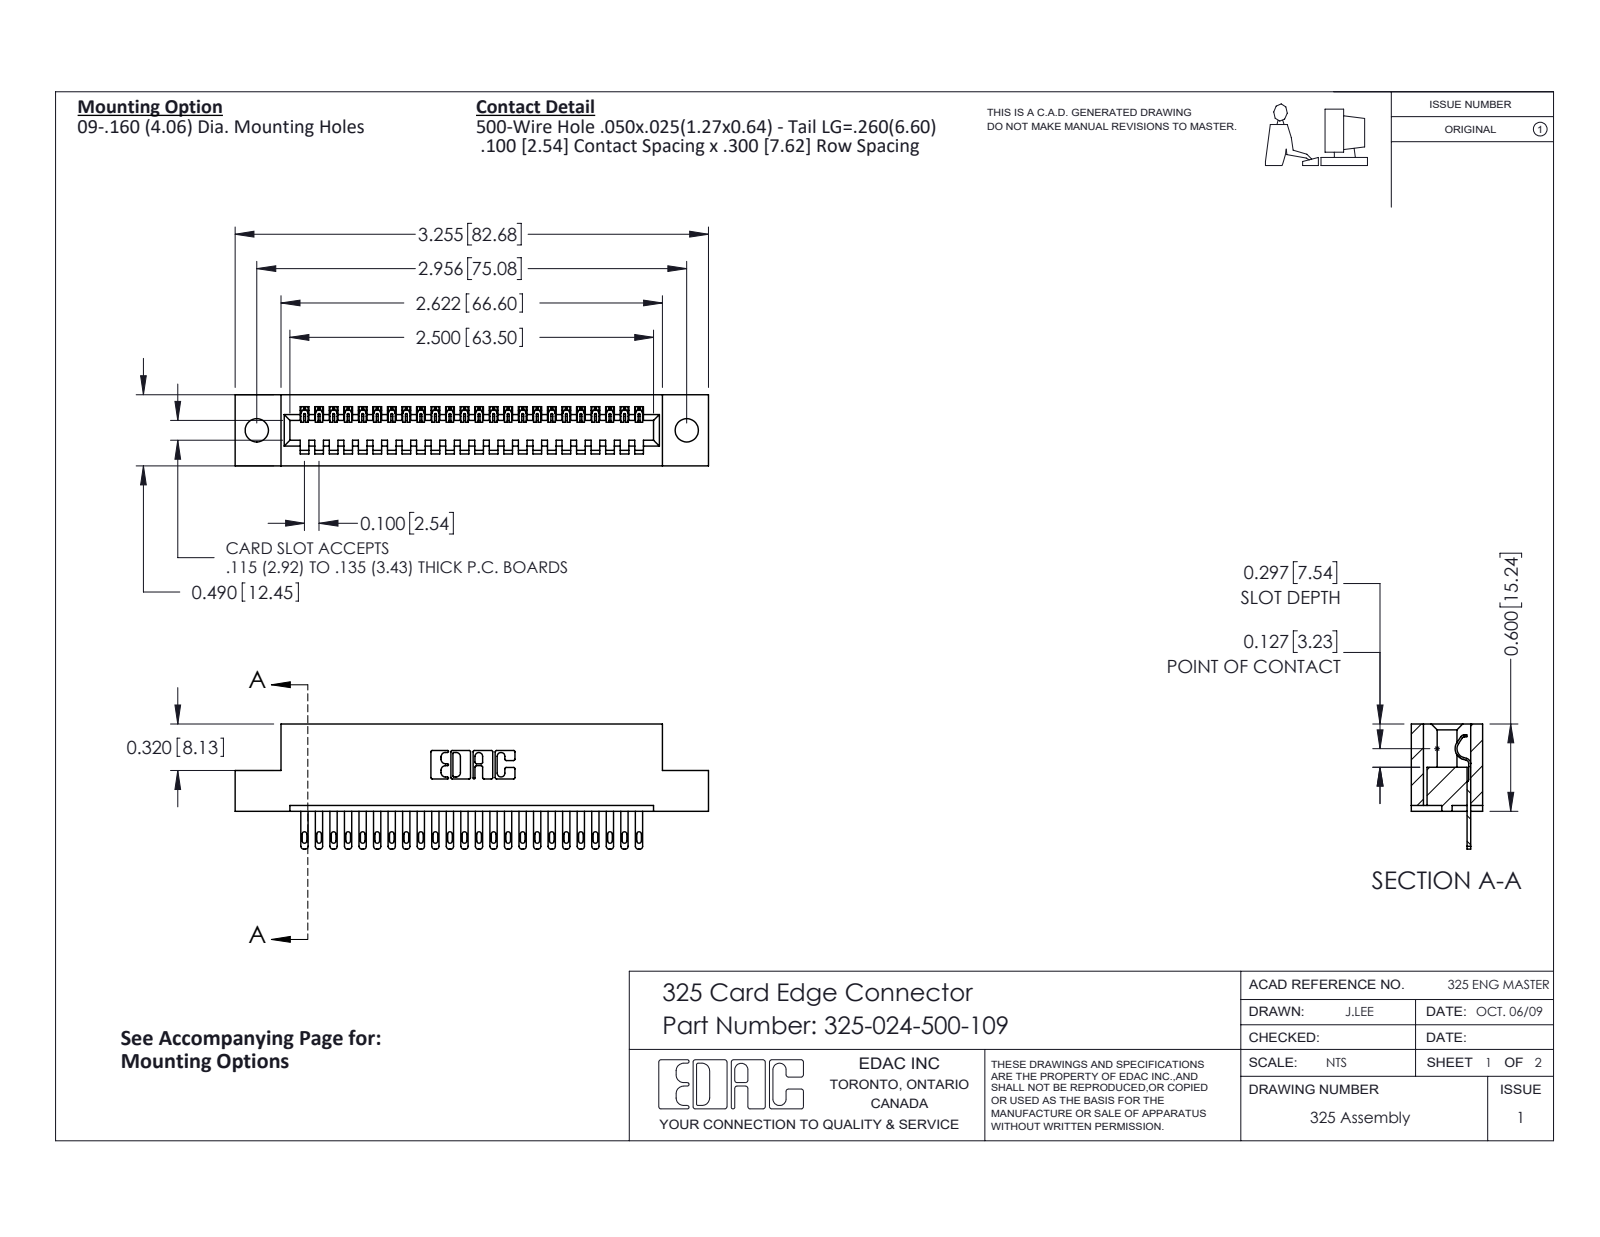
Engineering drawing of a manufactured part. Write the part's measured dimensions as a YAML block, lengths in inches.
part_name: "325-024-500-109; 325 Part_.160 TH; 325-292-001_325-293-100"
step_written_by: "SolidWorks 2016 (CONFIG_CONTROL_DESIGN)"
units: inches
bodies: {solids: 25, faces: 1410, planar: 934, cylindrical: 476, other: 0}
overall_size: [3.255, 0.86, 0.49]
volume: 0.619
surface_area: 16.62
round_holes:
  - {diameter: 0.16, count: 2}
partial_cylinders:
  - {radius: 0.006, count: 48}
  - {radius: 0.016, count: 48}
  - {radius: 0.02, count: 48}
  - {radius: 0.01, count: 22}
  - {radius: 0.007, count: 6}
  - {radius: 0.031, count: 6}
  - {radius: 0.026, count: 3}
  - {radius: 0.014, count: 1}
face_to_face_distances: [0.083, 0.407, 0.3, 0.49, 0.107, 0.383, 0.025, 0.04, 0.325, 0.6]
hole_center_spacings: [2.956]
